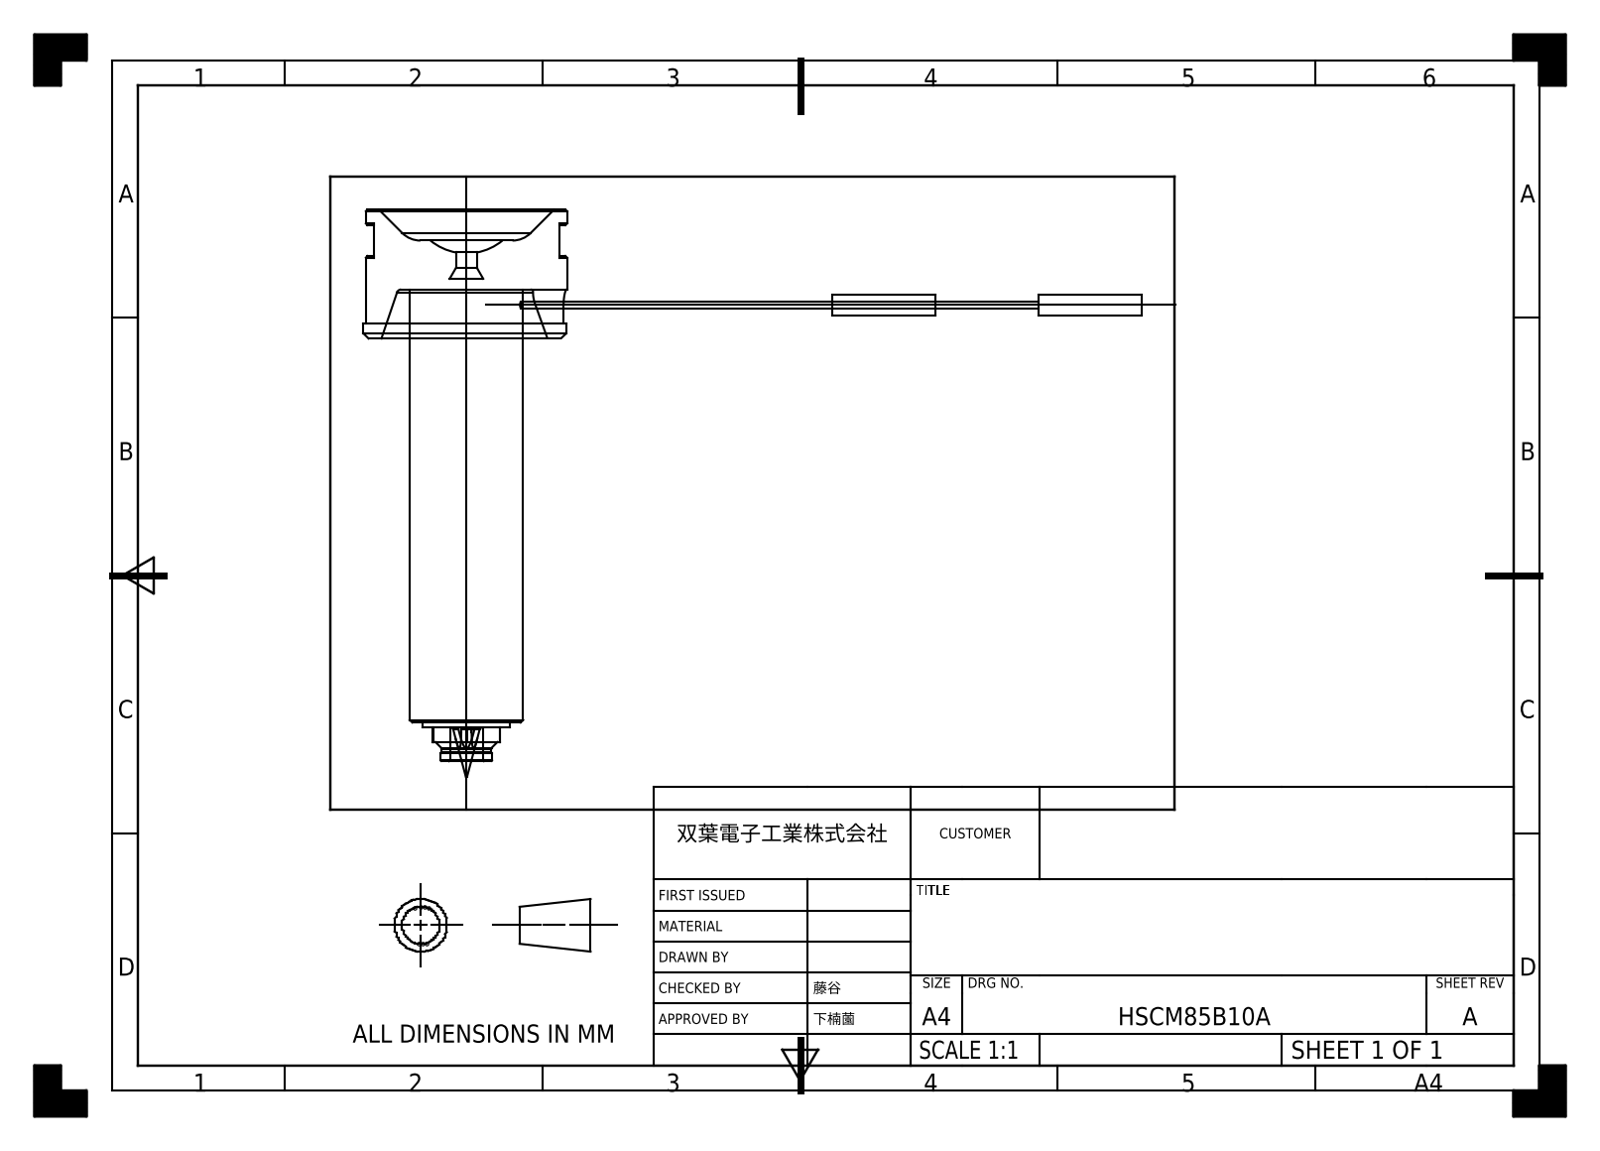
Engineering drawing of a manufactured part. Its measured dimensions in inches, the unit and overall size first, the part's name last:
Units: inches
Overall size (bounding box): 5.945 × 4.331 × 1.575
Round holes (diameter × count): ⌀0.157 ×1, ⌀0.25 ×1
Round bosses / shafts (diameter × count): ⌀0.157 ×2, ⌀0.047 ×2, ⌀1.575 ×1, ⌀1.535 ×1, ⌀0.866 ×1, ⌀0.665 ×1, ⌀0.394 ×1, ⌀0.378 ×1
Partial cylindrical surfaces — rounded edges, fillets, slot ends (radius × count): R0.11 ×3, R0.118 ×2, R0.293 ×1
Main face-to-face distances: 0.374, 0.984, 0.61, 3.346, 3.917, 3.307, 2.933, 0.118, 0.236, 0.748
Volume: 3.182 in³ · Surface area: 21.41 in²
Bodies: 1 solid, 75 faces (30 planar, 23 cylindrical, 22 other)
Part name (STEP PRODUCT): HSCM85B10A
STEP written by: SIEMENS PLM Software NX 2023 (AUTOMOTIVE_DESIGN)
